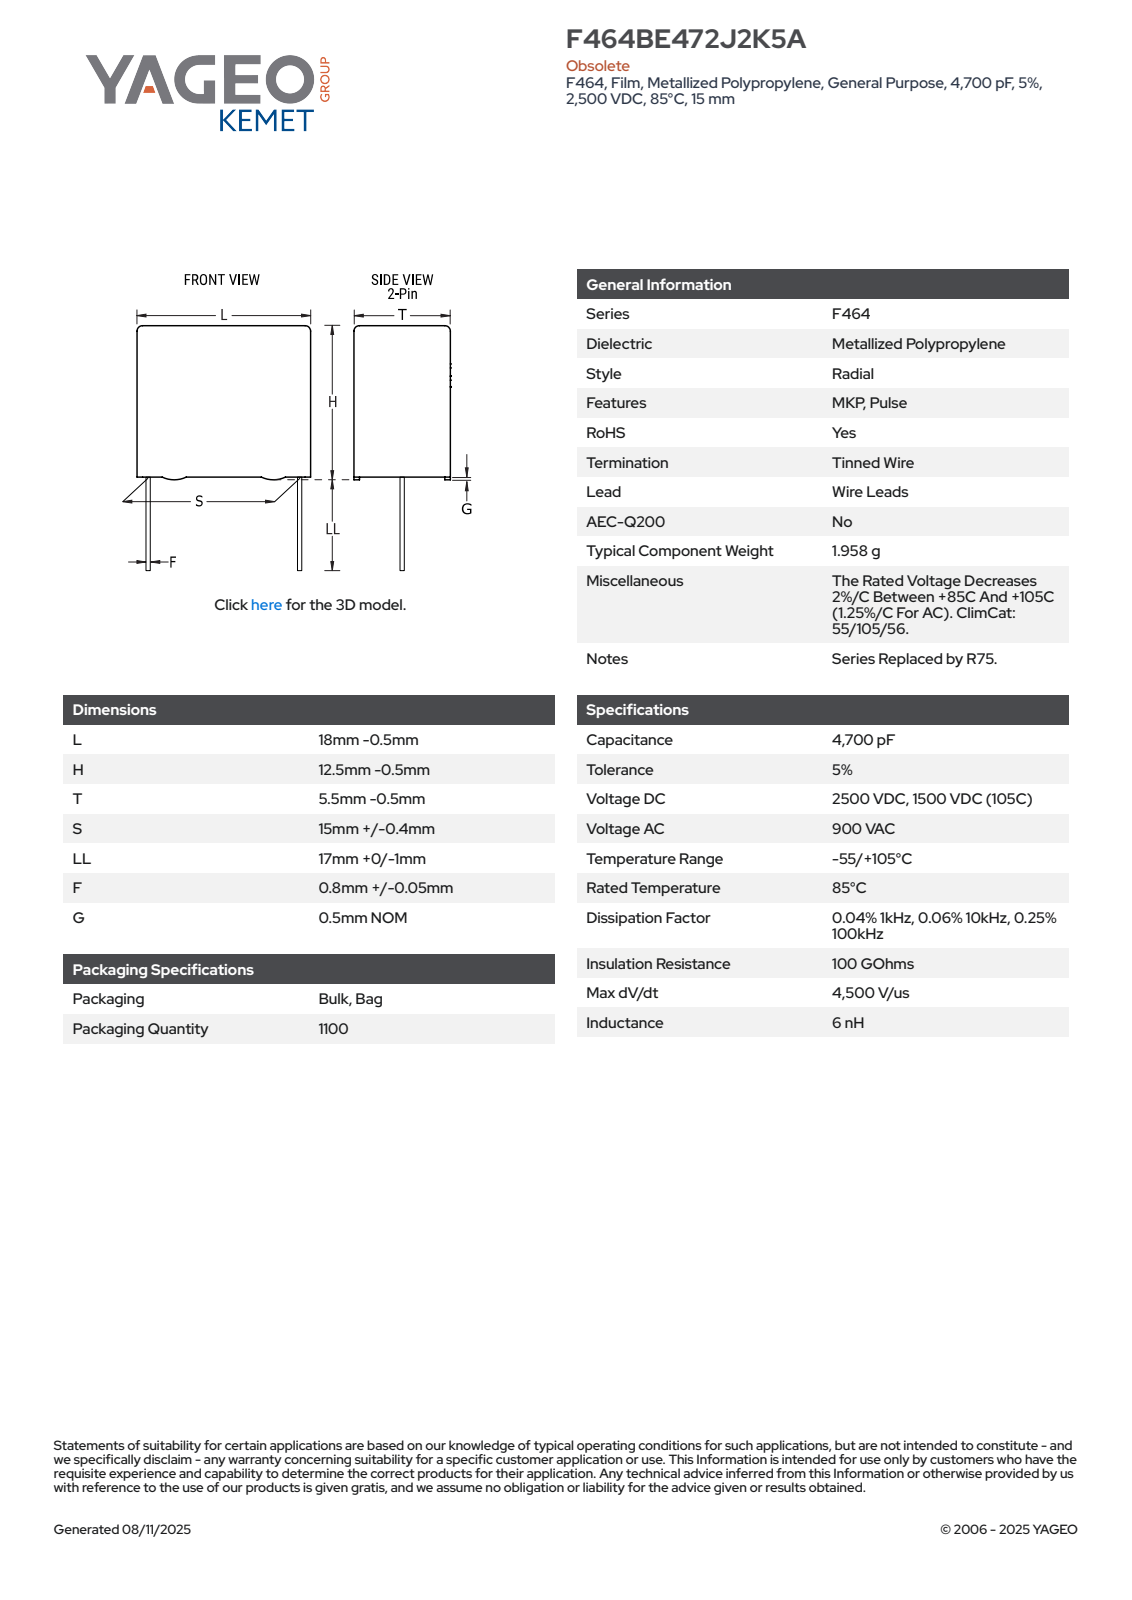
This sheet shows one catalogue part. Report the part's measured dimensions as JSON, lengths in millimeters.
{"part_name": "CFR_RBG_18X12.5X5.5_L17.5H12T5S15LL17F0.85G0.5", "step_written_by": "SolidWorks 2014 (AUTOMOTIVE_DESIGN)", "units": "millimeters", "bodies": {"solids": 4, "faces": 89, "planar": 81, "cylindrical": 8, "other": 0}, "overall_size": [29, 17.5, 5], "volume_mm3": 1025, "surface_area_mm2": 821, "round_bosses_or_shafts": [[0.85, 2]], "partial_cylinders_radius": [[0.5, 4]], "face_to_face_distances": [5, 11.5, 17.5, 0.5, 12, 4.72, 4.43, 4.71, 17, 29]}
